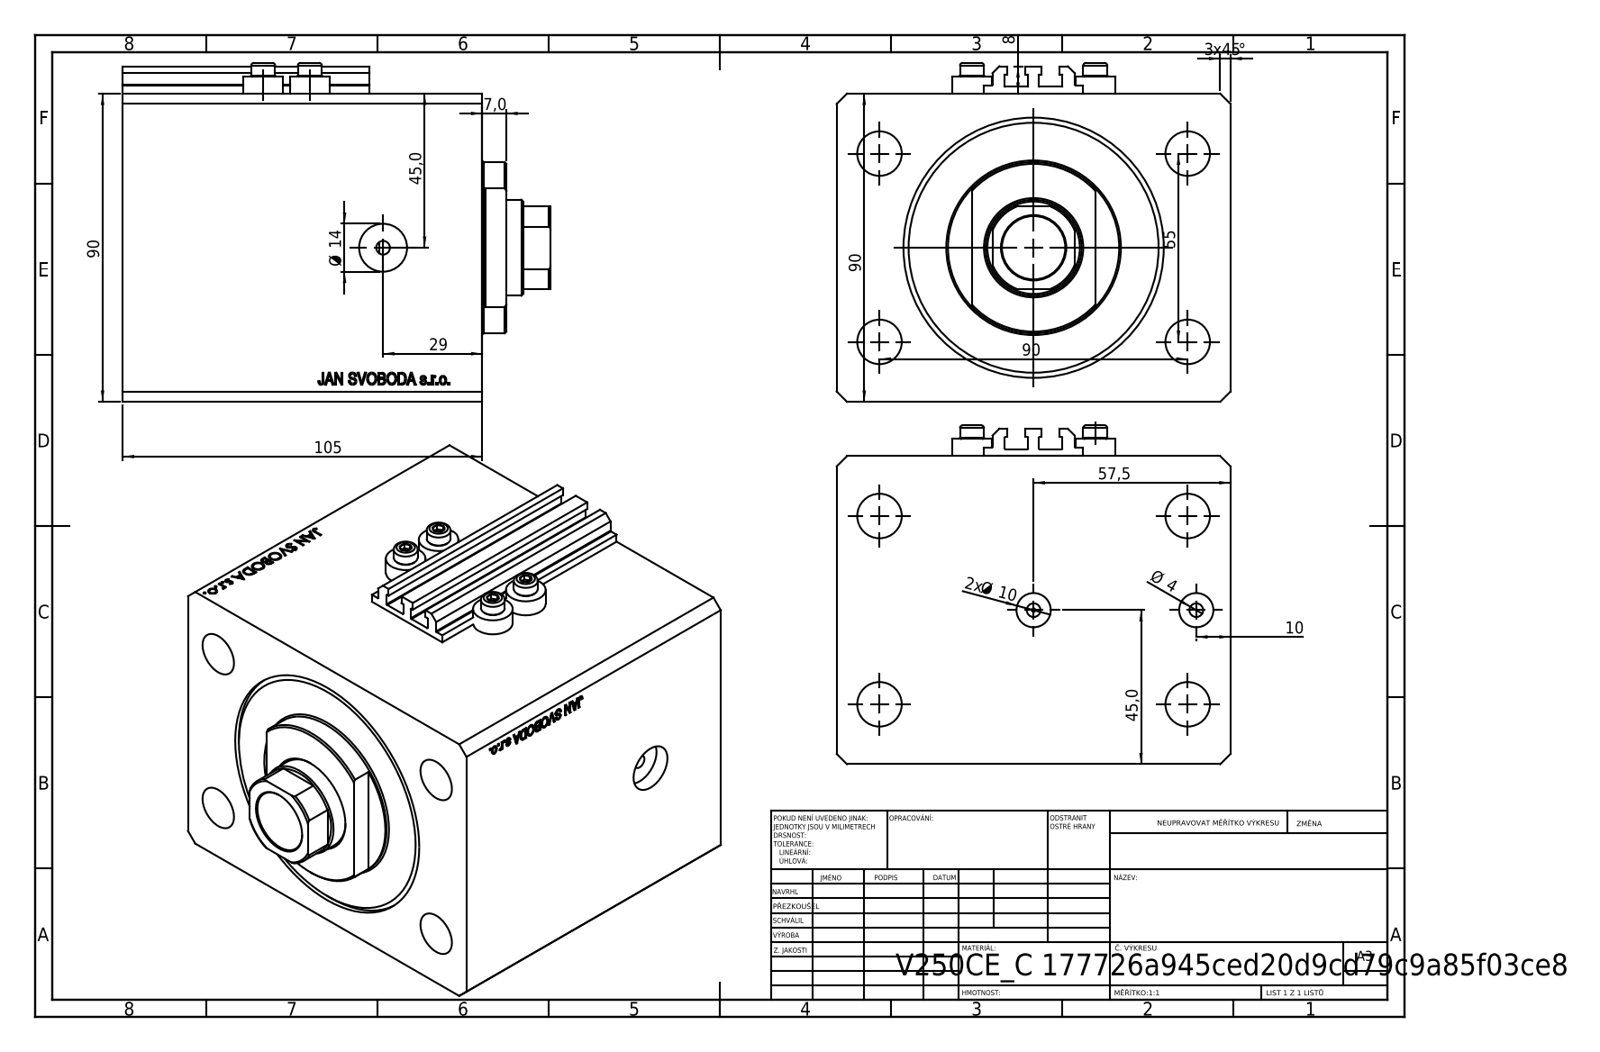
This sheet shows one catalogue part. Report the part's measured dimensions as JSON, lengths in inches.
{"part_name": "V250CE_VC_C; ALLEN BOLT V250CE; V250CE_C_VCP; V250CE_C_Body", "step_written_by": "SolidWorks 2019 (CONFIG_CONTROL_DESIGN)", "units": "inches", "bodies": {"solids": 8, "faces": 1038, "planar": 504, "cylindrical": 88, "other": 446}, "overall_size": [4.917, 4.528, 3.898], "volume_in3": 60.8, "surface_area_in2": 233.6, "round_holes": [[0.157, 8], [0.512, 4], [0.394, 2], [0.551, 2], [0.049, 1], [0.728, 1], [1.102, 1], [2.48, 1], [2.992, 1]], "round_bosses_or_shafts": [[0.457, 4], [0.276, 4], [1.969, 1]], "partial_cylinders_radius": [[0.008, 10], [0.531, 1]], "face_to_face_distances": [3.543, 4.528, 4.134, 3.429, 0.705, 2.244, 2.949, 1.185, 2.161, 1.457], "hole_center_spacings": [2.076, 0.535, 1.087, 1.417, 1.515, 2.165, 3.543, 3.799]}
